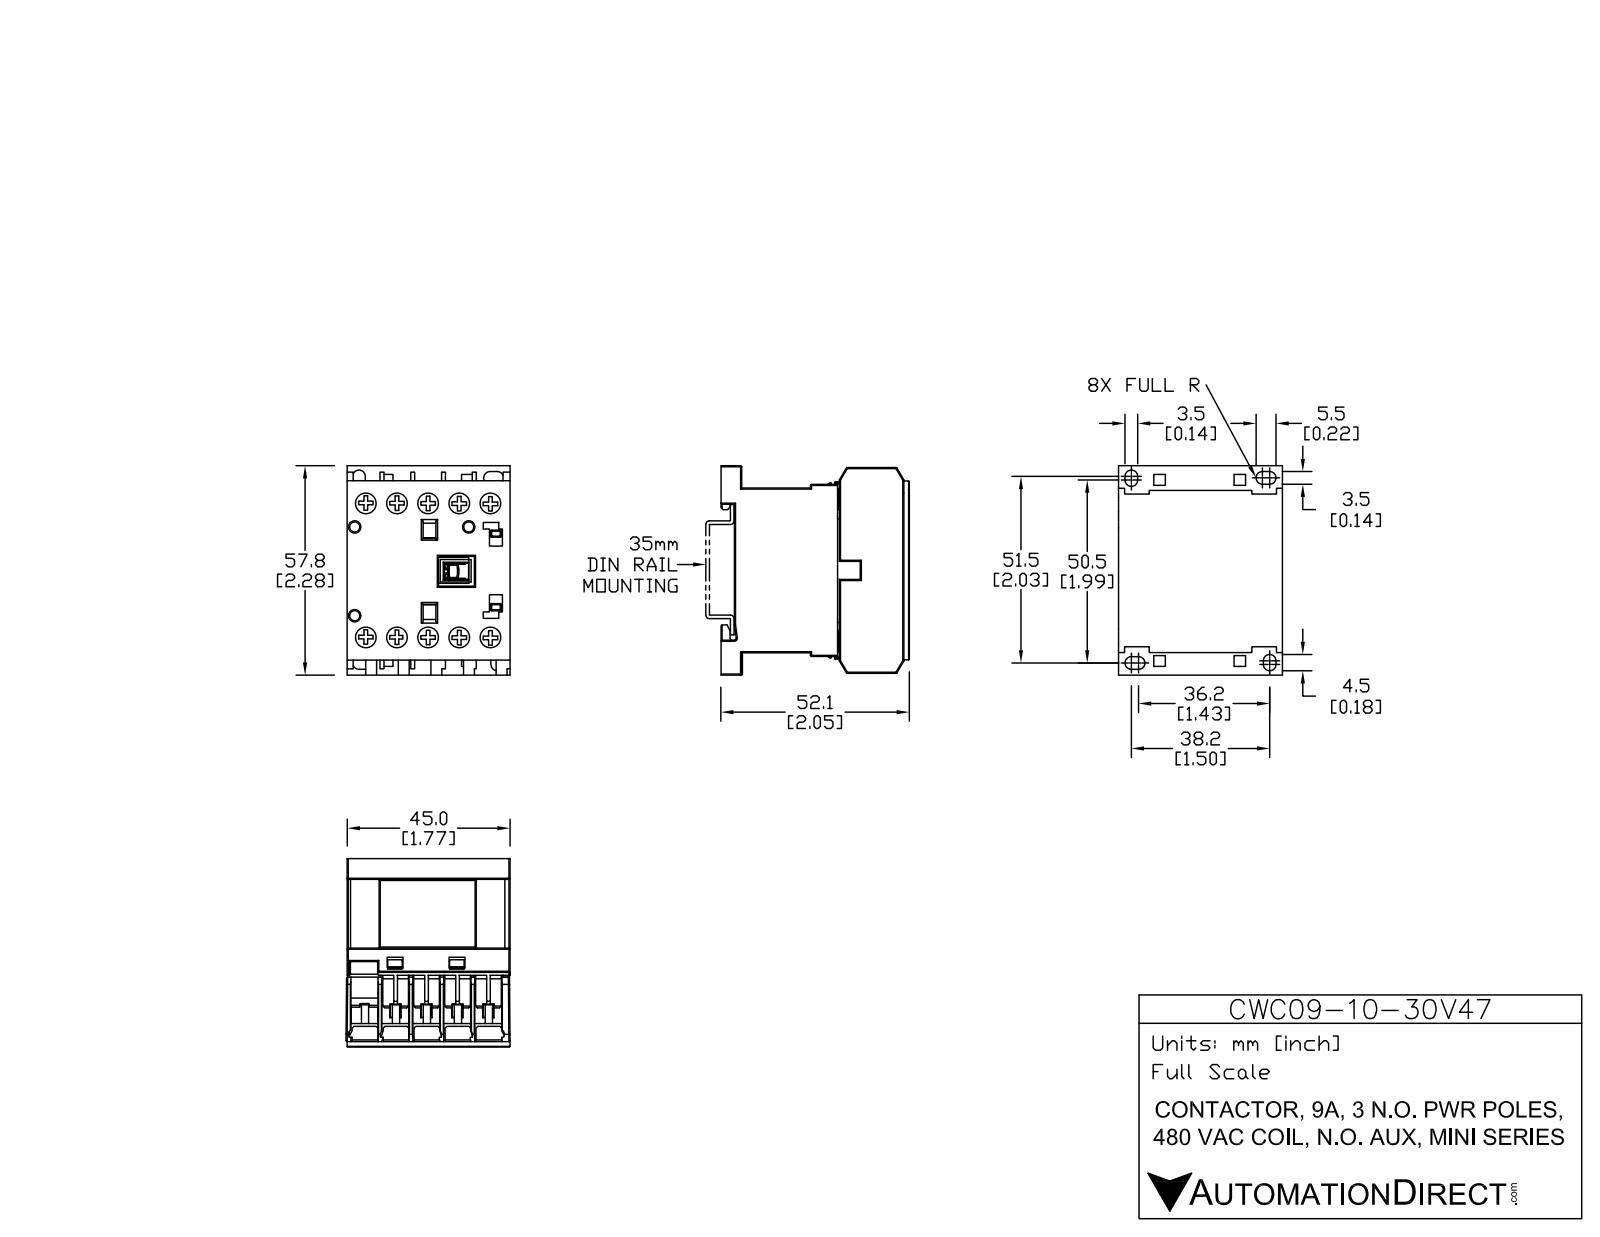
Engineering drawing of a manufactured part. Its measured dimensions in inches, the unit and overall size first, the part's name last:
Units: inches
Overall size (bounding box): 2.285 × 2.052 × 1.801
Round holes (diameter × count): ⌀0.244 ×10, ⌀0.11 ×3
Round bosses / shafts (diameter × count): ⌀0.232 ×10
Partial cylindrical surfaces — rounded edges, fillets, slot ends (radius × count): R0.012 ×20, R0.068 ×6, R0.068 ×2, R0.013 ×1, R0.017 ×1, R0.022 ×1
Main face-to-face distances: 0.325, 1.791, 0.049, 0.65, 0.374, 0.217, 0.699, 0.202, 0.419, 0.276
Hole centre spacings: 0.337, 1.494, 0.673, 1.603, 1.455, 1.01, 1.771, 0.272
Volume: 5.927 in³ · Surface area: 47.18 in²
Bodies: 15 solids, 535 faces (445 planar, 90 cylindrical, 0 other)
Part name (STEP PRODUCT): CWC09-10-30V47
STEP written by: SolidWorks 2013 (AUTOMOTIVE_DESIGN)
